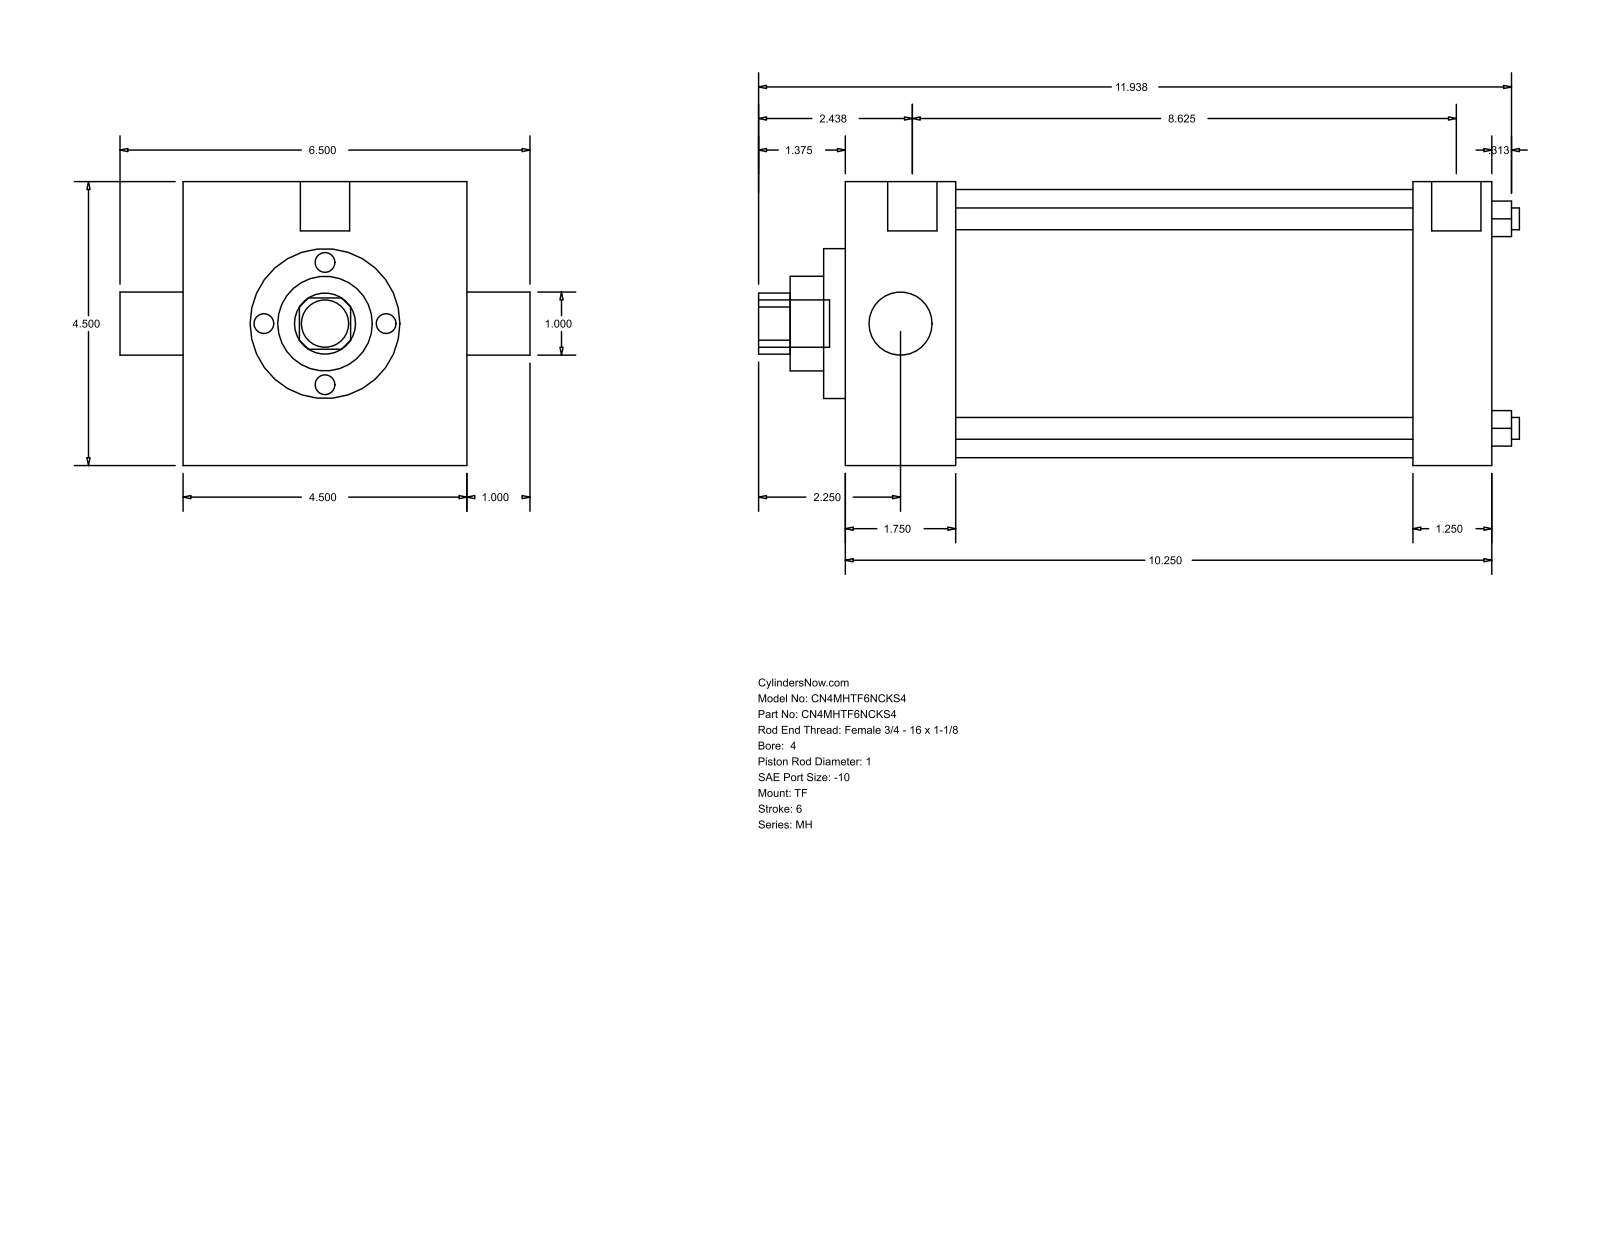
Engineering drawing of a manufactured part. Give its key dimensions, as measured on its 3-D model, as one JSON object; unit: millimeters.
{"part_name": "MH_TF__0400_1", "step_written_by": "GSSL Pune (CONFIG_CONTROL_DESIGN)", "units": "millimeters", "bodies": {"solids": 0, "faces": 86, "planar": 61, "cylindrical": 25, "other": 0}, "overall_size": [306.39, 165.1, 114.3], "round_holes": [[8.76, 4], [25.4, 2], [38.1, 1], [60.33, 1], [107.95, 1]], "round_bosses_or_shafts": [[8.73, 3], [19.84, 2], [19.05, 1]], "partial_cylinders_radius": [[12.29, 1]], "face_to_face_distances": [114.3, 260.35, 44.46, 215.89, 228.6, 184.14, 31.75, 8.73, 53.19, 237.33], "hole_center_spacings": [59.62, 84.32, 119.25]}
